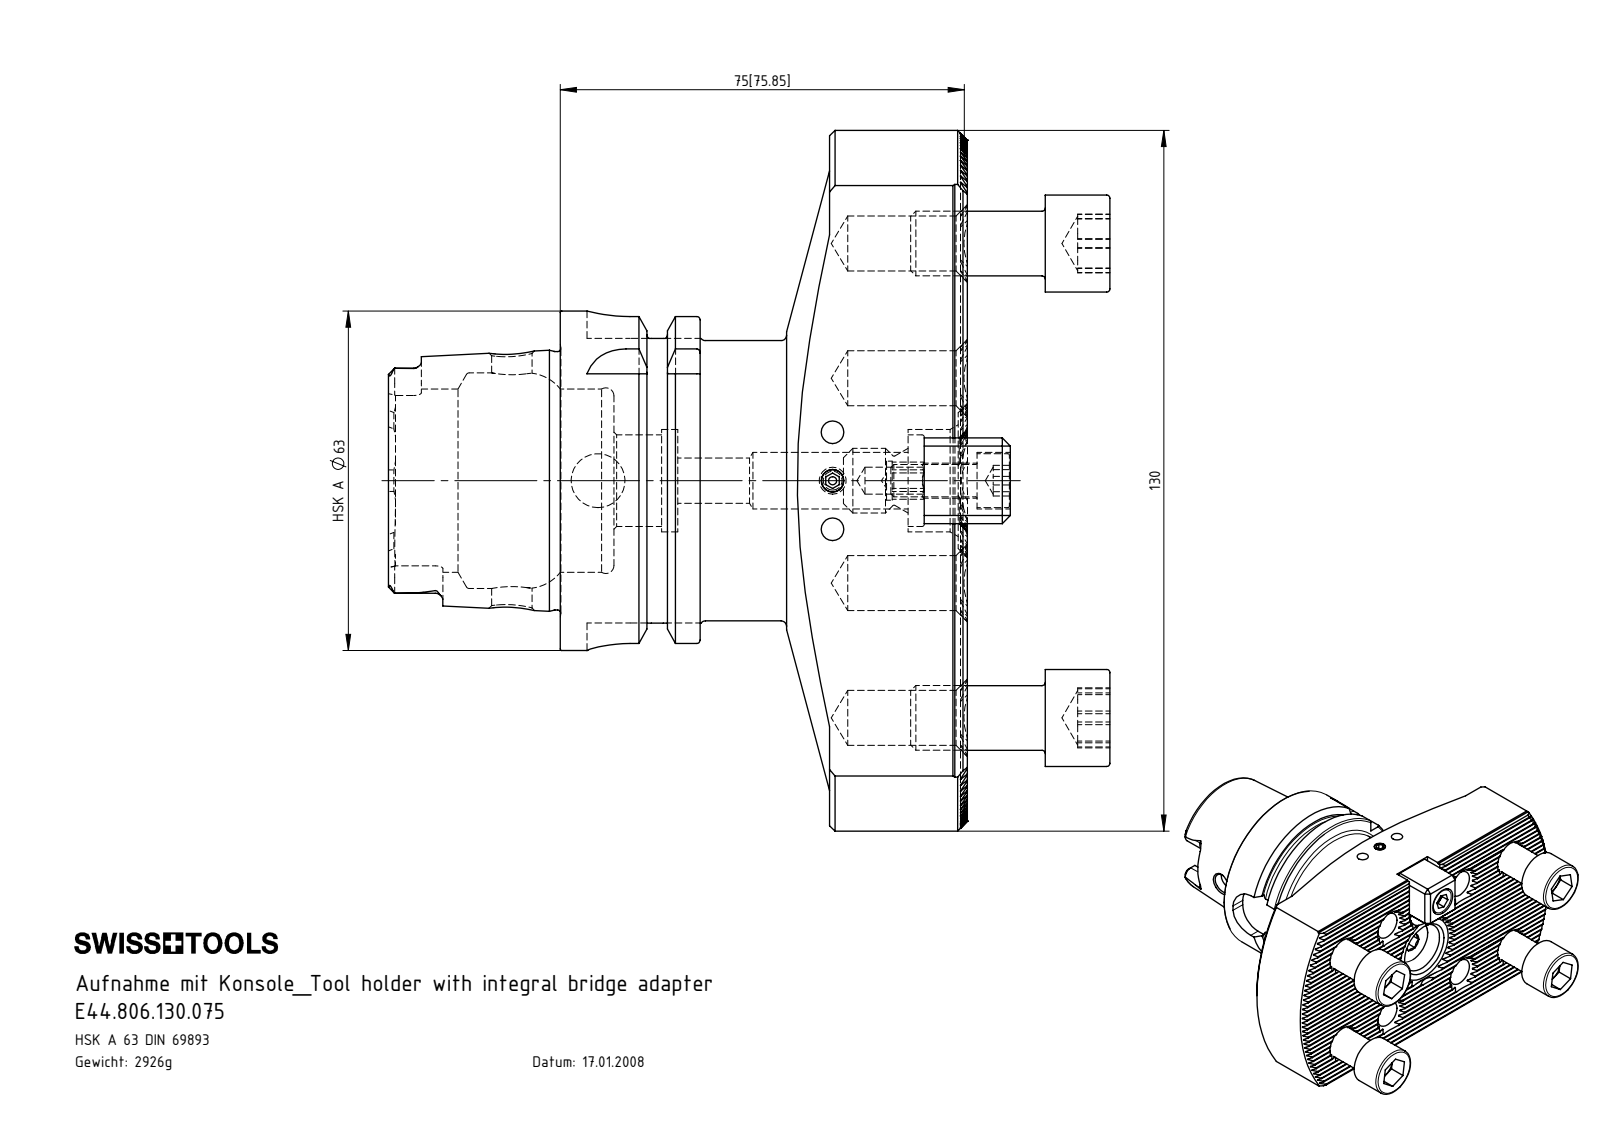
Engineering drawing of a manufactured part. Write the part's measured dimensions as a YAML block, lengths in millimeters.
part_name: "Ko1-ER1.001.016_A; HA6-Ko1.K01.075_A_Fertigbearbeitung; ISO 4762 M12 x 25; ISO 4026 - M5 x 8_ISO 4026 - M5 x 8 (+3 more)"
step_written_by: "SolidWorks 2017 (CONFIG_CONTROL_DESIGN)"
units: millimeters
bodies: {solids: 10, faces: 945, planar: 517, cylindrical: 226, other: 202}
overall_size: [133.93, 130, 70]
volume: 372684
surface_area: 74529
round_holes:
  - {diameter: 10.2, count: 8}
  - {diameter: 4.2, count: 3}
  - {diameter: 10.5, count: 2}
  - {diameter: 1.5, count: 1}
  - {diameter: 5, count: 1}
  - {diameter: 6.5, count: 1}
  - {diameter: 7.24, count: 1}
  - {diameter: 7.5, count: 1}
  - {diameter: 8.4, count: 1}
  - {diameter: 10, count: 1}
  - {diameter: 17, count: 1}
  - {diameter: 19, count: 1}
round_bosses_or_shafts:
  - {diameter: 12, count: 5}
  - {diameter: 18, count: 4}
  - {diameter: 63, count: 1}
  - {diameter: 54.95, count: 1}
  - {diameter: 52, count: 1}
  - {diameter: 47.94, count: 1}
  - {diameter: 10, count: 1}
  - {diameter: 6, count: 1}
partial_cylinders:
  - {radius: 0.14, count: 34}
  - {radius: 1.4, count: 6}
  - {radius: 2.88, count: 4}
  - {radius: 8, count: 4}
  - {radius: 7.95, count: 1}
  - {radius: 65, count: 1}
face_to_face_distances: [1.73, 17.32, 70, 8.66, 3.46, 5.2, 6.93, 15.59, 19.05, 3.47]
hole_center_spacings: [25, 27.59, 40, 47.17, 48.33, 63, 74.63, 9]
